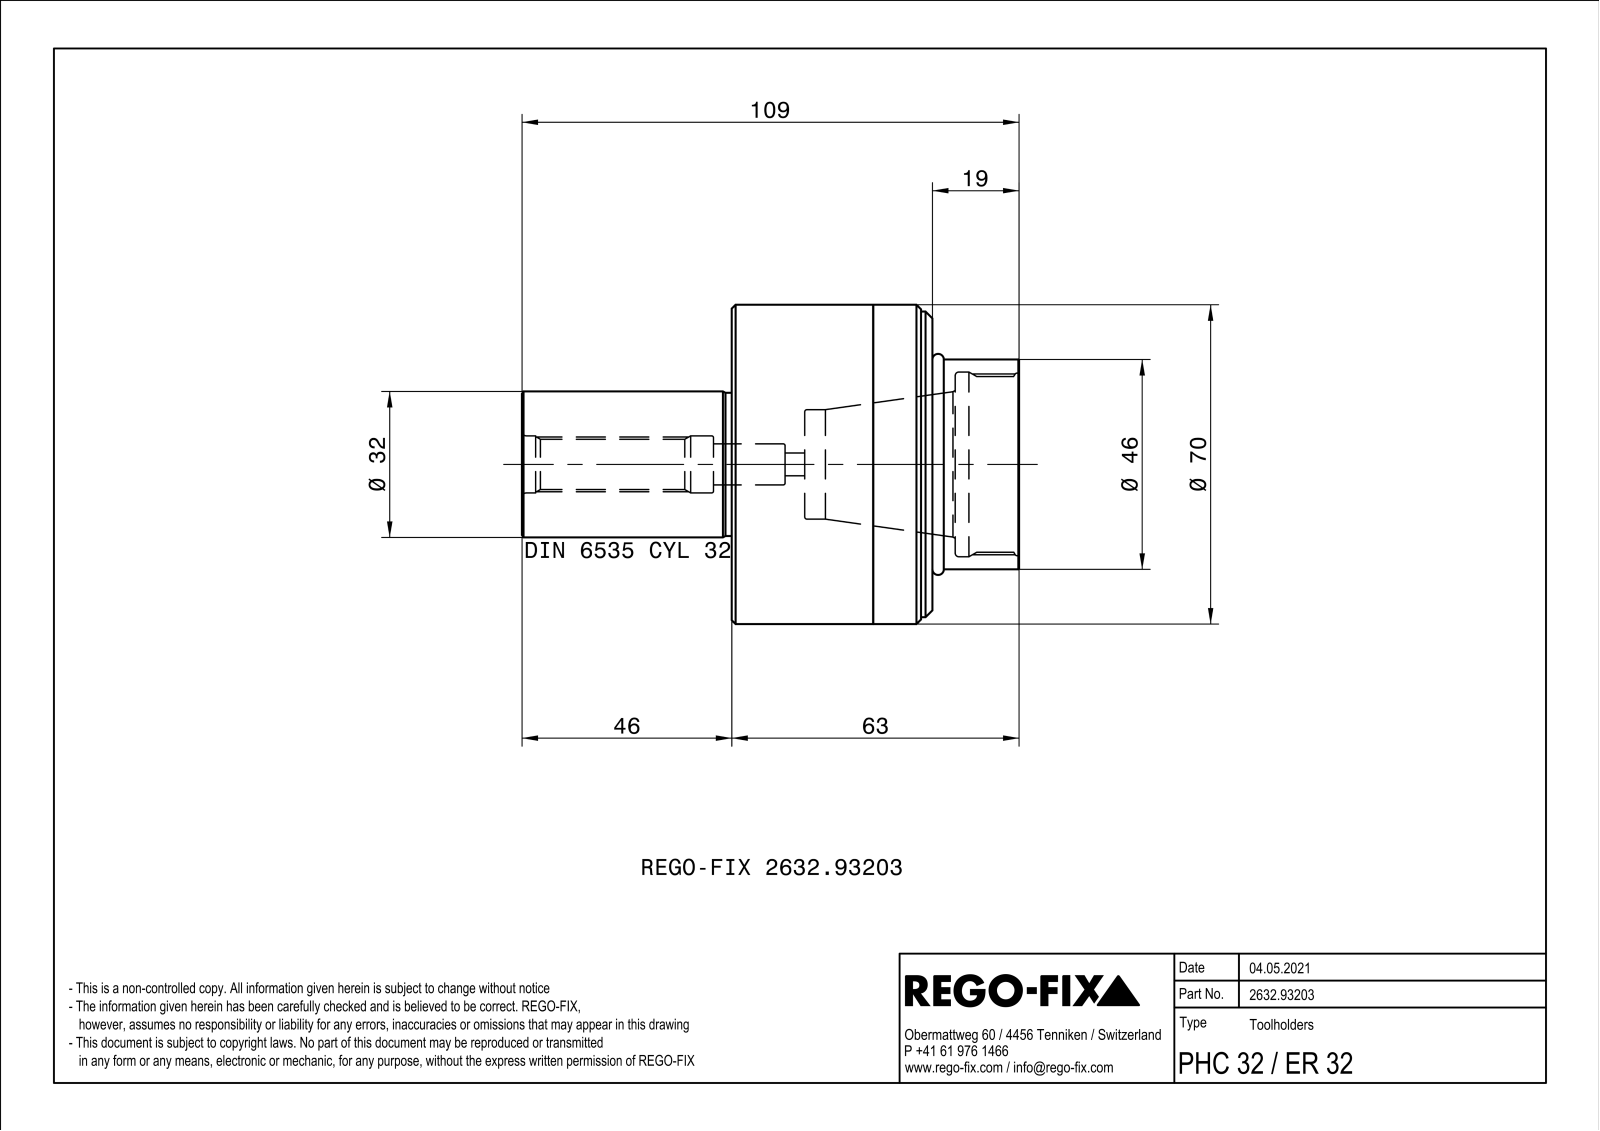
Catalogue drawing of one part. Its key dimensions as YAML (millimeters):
part_name: "NOCUT"
step_written_by: "SIEMENS PLM Software Solid Edge ST10 (AUTOMOTIVE_DESIGN)"
units: millimeters
bodies: {solids: 1, faces: 128, planar: 27, cylindrical: 37, other: 64}
overall_size: [109, 70, 70]
volume: 158013
surface_area: 54291
round_holes:
  - {diameter: 5, count: 4}
  - {diameter: 2.11, count: 1}
  - {diameter: 3.2, count: 1}
  - {diameter: 5.2, count: 1}
  - {diameter: 7.4, count: 1}
  - {diameter: 9, count: 1}
  - {diameter: 11, count: 1}
  - {diameter: 12.5, count: 1}
  - {diameter: 24, count: 1}
  - {diameter: 38.5, count: 1}
  - {diameter: 40.5, count: 1}
  - {diameter: 46, count: 1}
round_bosses_or_shafts:
  - {diameter: 70, count: 1}
  - {diameter: 67, count: 1}
  - {diameter: 60, count: 1}
  - {diameter: 58.5, count: 1}
  - {diameter: 58.4, count: 1}
  - {diameter: 54, count: 1}
  - {diameter: 53.4, count: 1}
  - {diameter: 36, count: 1}
face_to_face_distances: [6, 12, 5.7, 12.3, 6.3, 26, 18, 32, 44, 38.3]
hole_center_spacings: [24, 33.94, 48, 27.8]
